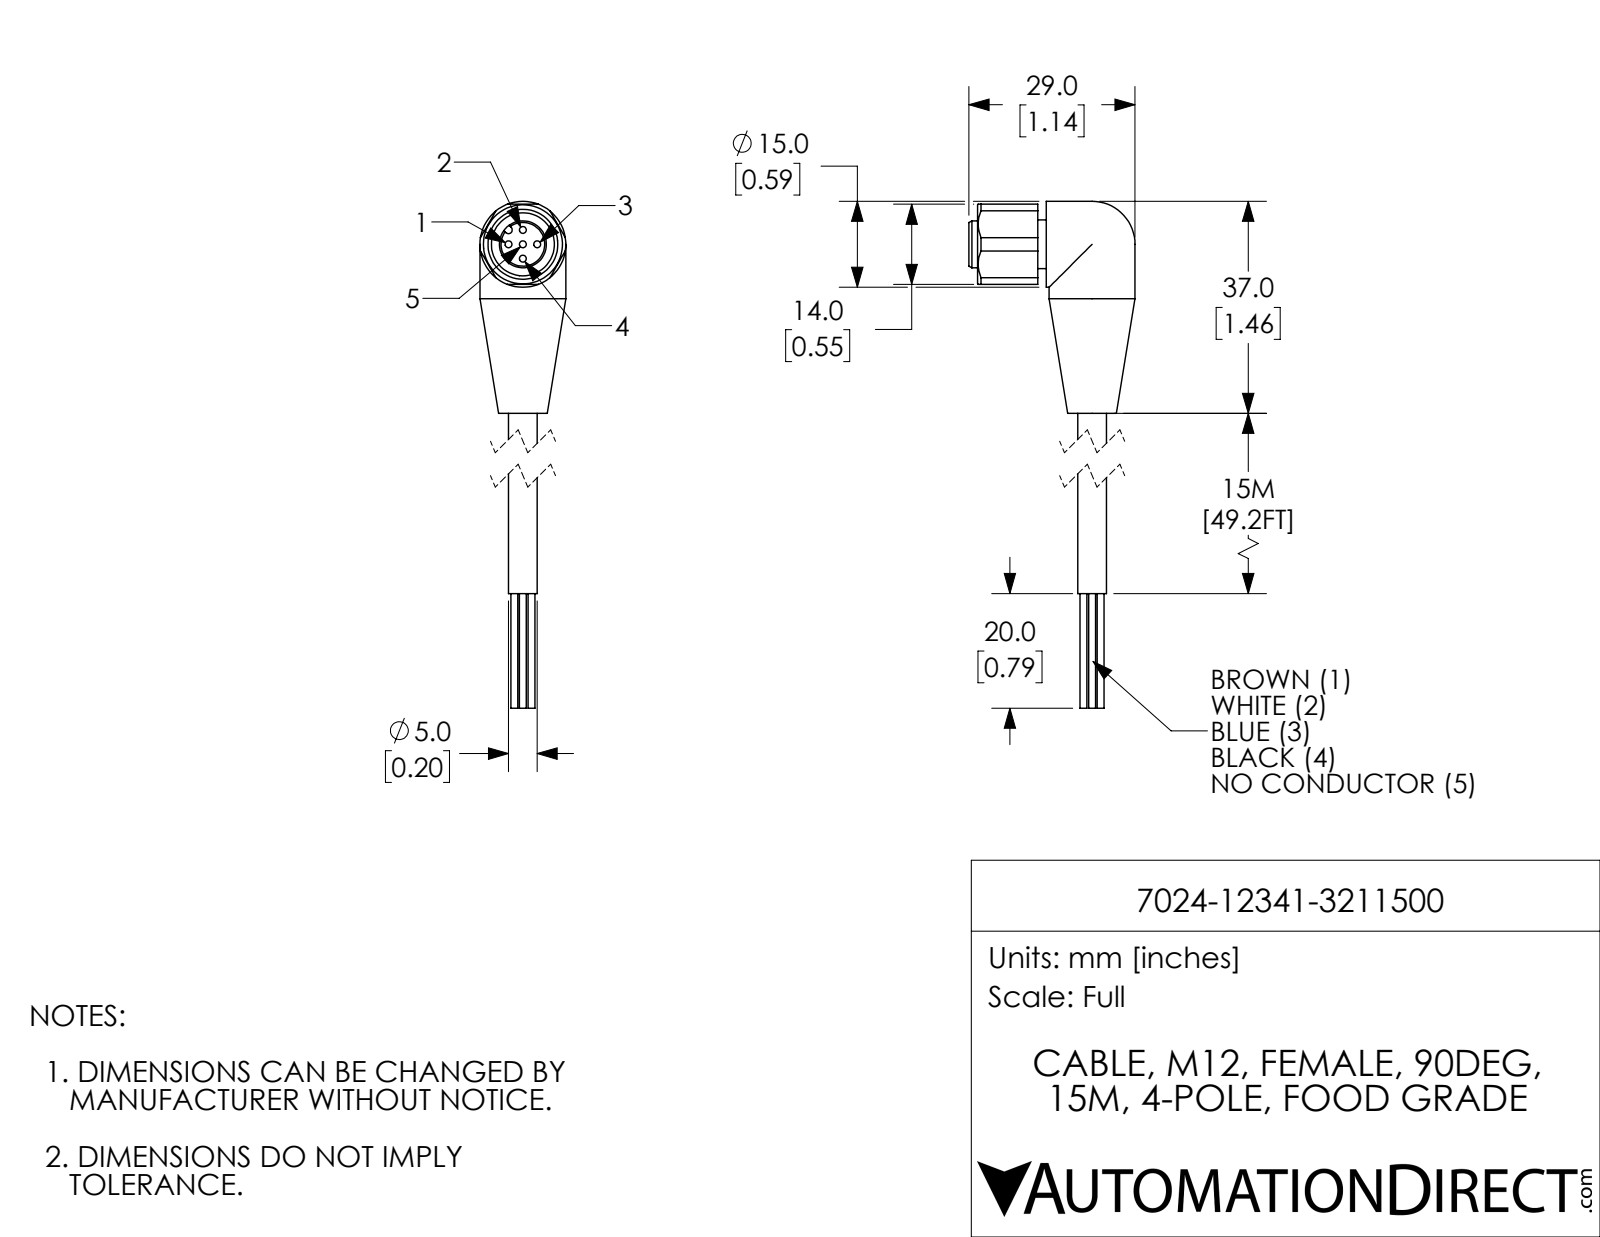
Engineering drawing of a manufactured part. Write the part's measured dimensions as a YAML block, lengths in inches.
part_name: "7024-12341-3211500"
step_written_by: "SolidWorks 2018 (AUTOMOTIVE_DESIGN)"
units: inches
bodies: {solids: 1, faces: 73, planar: 25, cylindrical: 38, other: 10}
overall_size: [3.425, 1.142, 0.591]
volume: 0.452
surface_area: 6.023
round_holes:
  - {diameter: 0.047, count: 5}
  - {diameter: 0.433, count: 1}
round_bosses_or_shafts:
  - {diameter: 0.047, count: 4}
  - {diameter: 0.591, count: 2}
  - {diameter: 0.335, count: 1}
  - {diameter: 0.323, count: 1}
  - {diameter: 0.197, count: 1}
partial_cylinders:
  - {radius: 0.026, count: 1}
face_to_face_distances: [0.551, 0.059, 0.472, 0.177, 0.118, 0.531, 0.354, 0.886, 1.437, 0.413]
hole_center_spacings: [0.098, 0.139, 0.197]
